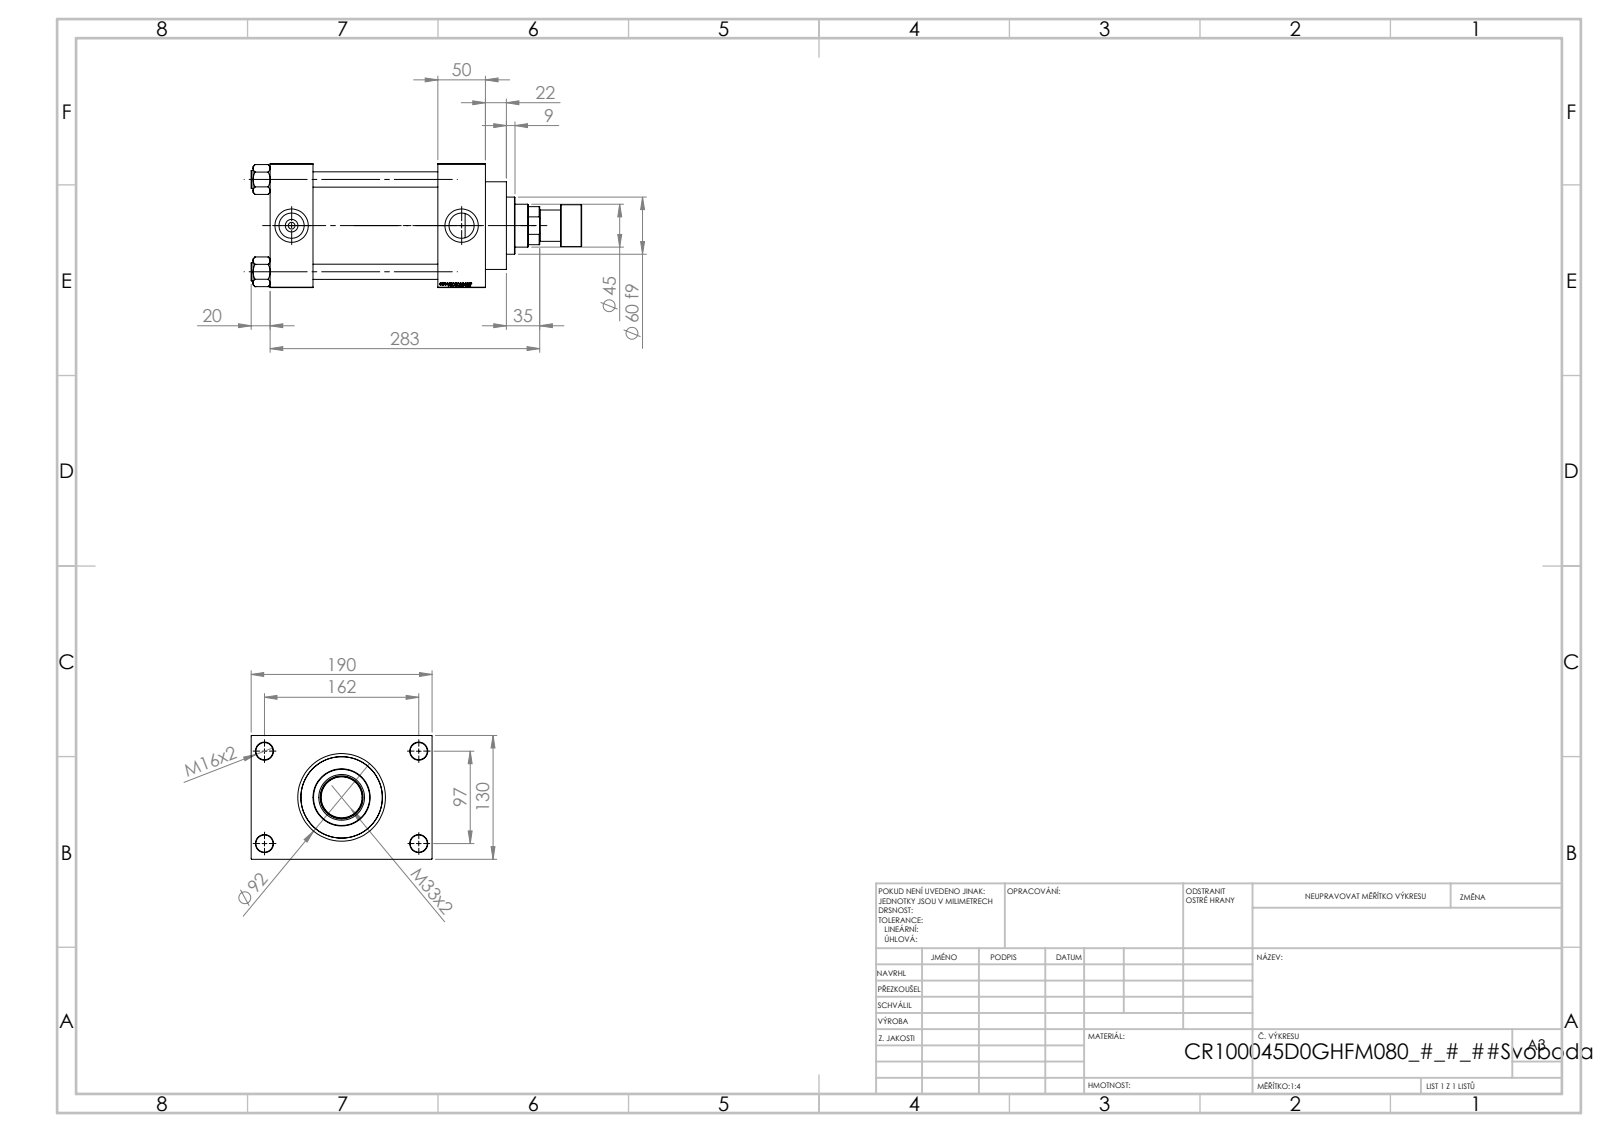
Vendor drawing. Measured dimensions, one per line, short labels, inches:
name: V215_VC_A; V215CR_ROD_END_F; NUT_M5_D; V215CR_D_Body (+2 more)
written by: SolidWorks 2019 (CONFIG_CONTROL_DESIGN)
unit: in
bodies: 12 solids, 1164 faces (548 planar, 92 cylindrical, 524 other)
size: 13.661 × 7.48 × 5.118
volume: 173.6 in³; area: 655.1 in²
holes: 4× ⌀0.63, 4× ⌀0.709, 2× ⌀0.276, 2× ⌀1.041, 2× ⌀1.378, 1× ⌀1.24, 1× ⌀1.772, 1× ⌀1.89, 1× ⌀2.992, 1× ⌀3.366, 1× ⌀3.937
bosses: 4× ⌀0.748, 1× ⌀4.173, 1× ⌀3.622, 1× ⌀2.362, 1× ⌀1.732, 1× ⌀1.299
face distances: 5.118, 1.772, 6.929, 5.157, 8.898, 7.126, 1.969, 1.181, 6.299, 3.15
hole spacings: 1.281, 2.698, 3.717, 3.815, 4.026, 5.096, 6.367, 3.819
